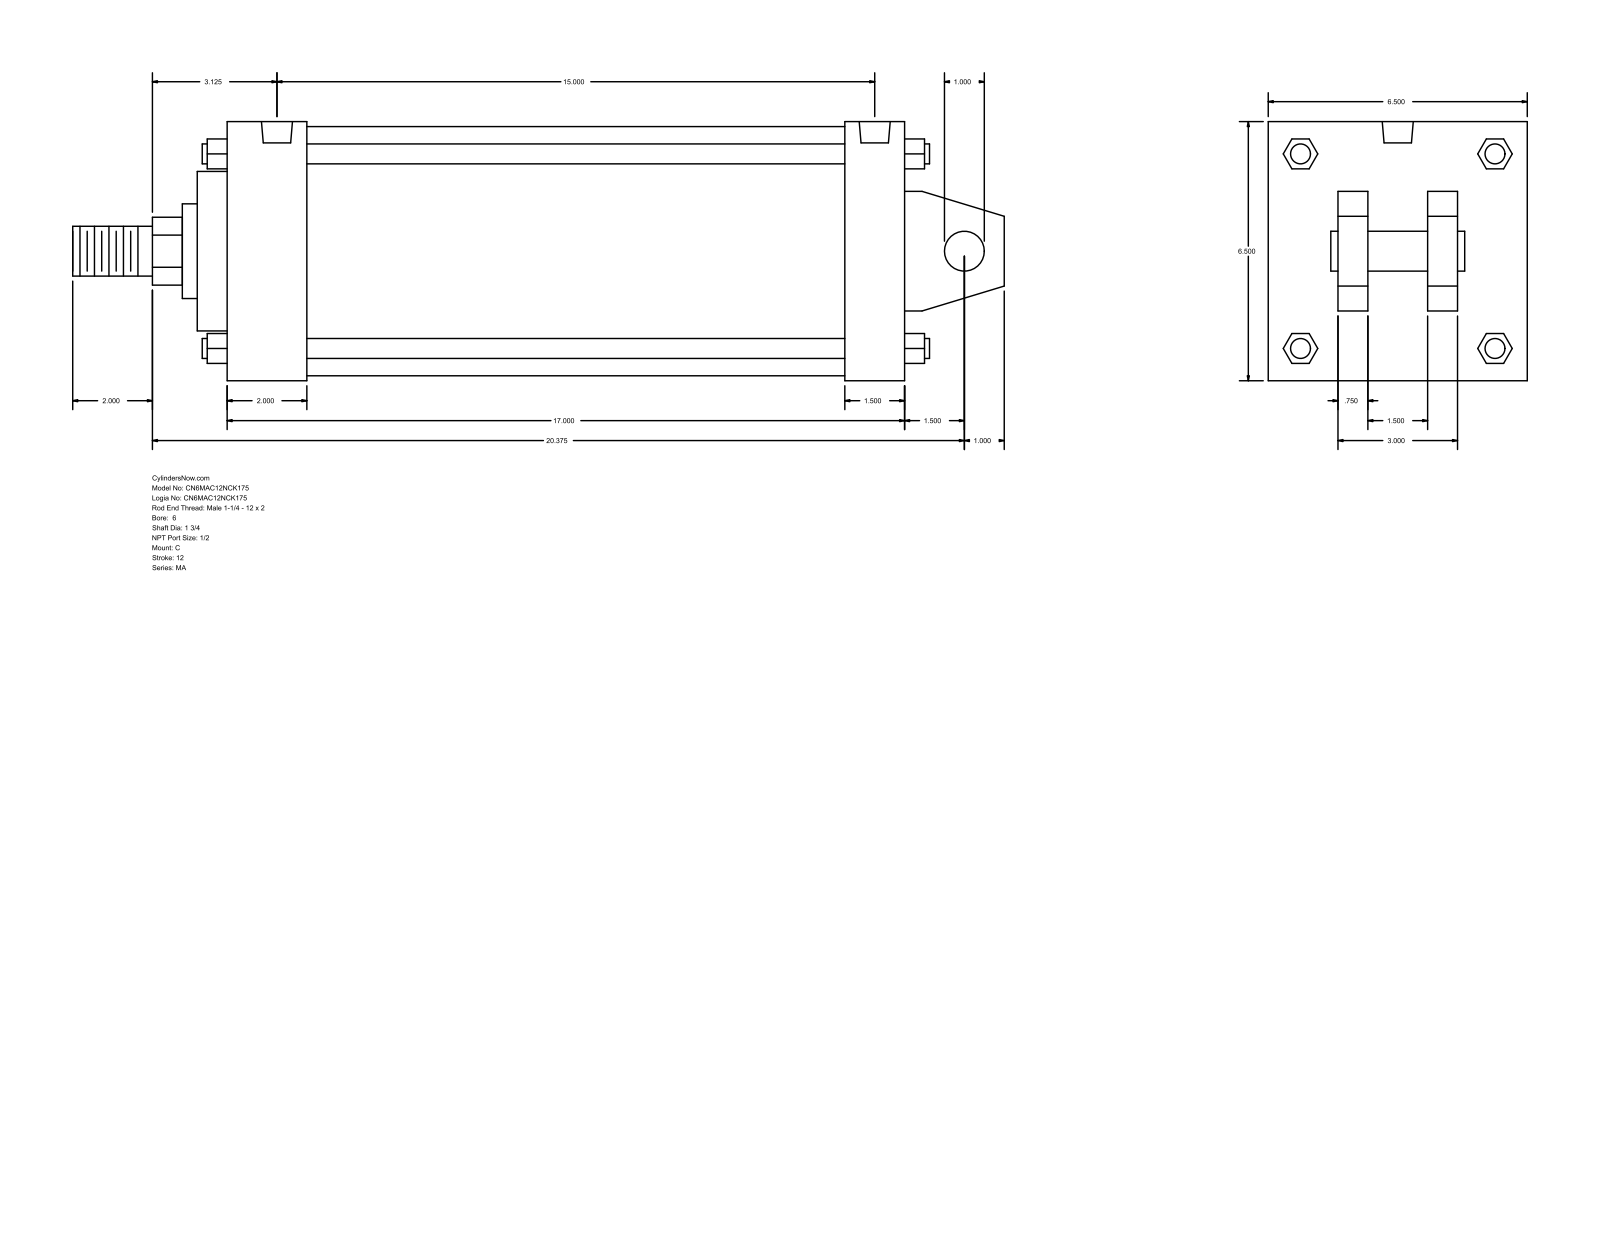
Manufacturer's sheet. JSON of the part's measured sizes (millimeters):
{"part_name": "MA_C__0600_1.75", "step_written_by": "GSSL Pune (CONFIG_CONTROL_DESIGN)", "units": "millimeters", "bodies": {"solids": 0, "faces": 141, "planar": 109, "cylindrical": 32, "other": 0}, "overall_size": [593.73, 165.1, 165.1], "round_holes": [[17.46, 4], [19.77, 2]], "round_bosses_or_shafts": [[12.7, 4], [158.75, 1], [101.6, 1], [60.33, 1], [44.45, 1], [31.75, 1], [25.4, 1]], "partial_cylinders_radius": [[21.63, 1]], "face_to_face_distances": [165.1, 431.81, 19.05, 101.6, 63.5, 50.8, 44.45, 120.65, 393.7, 57.15], "hole_center_spacings": [381]}
